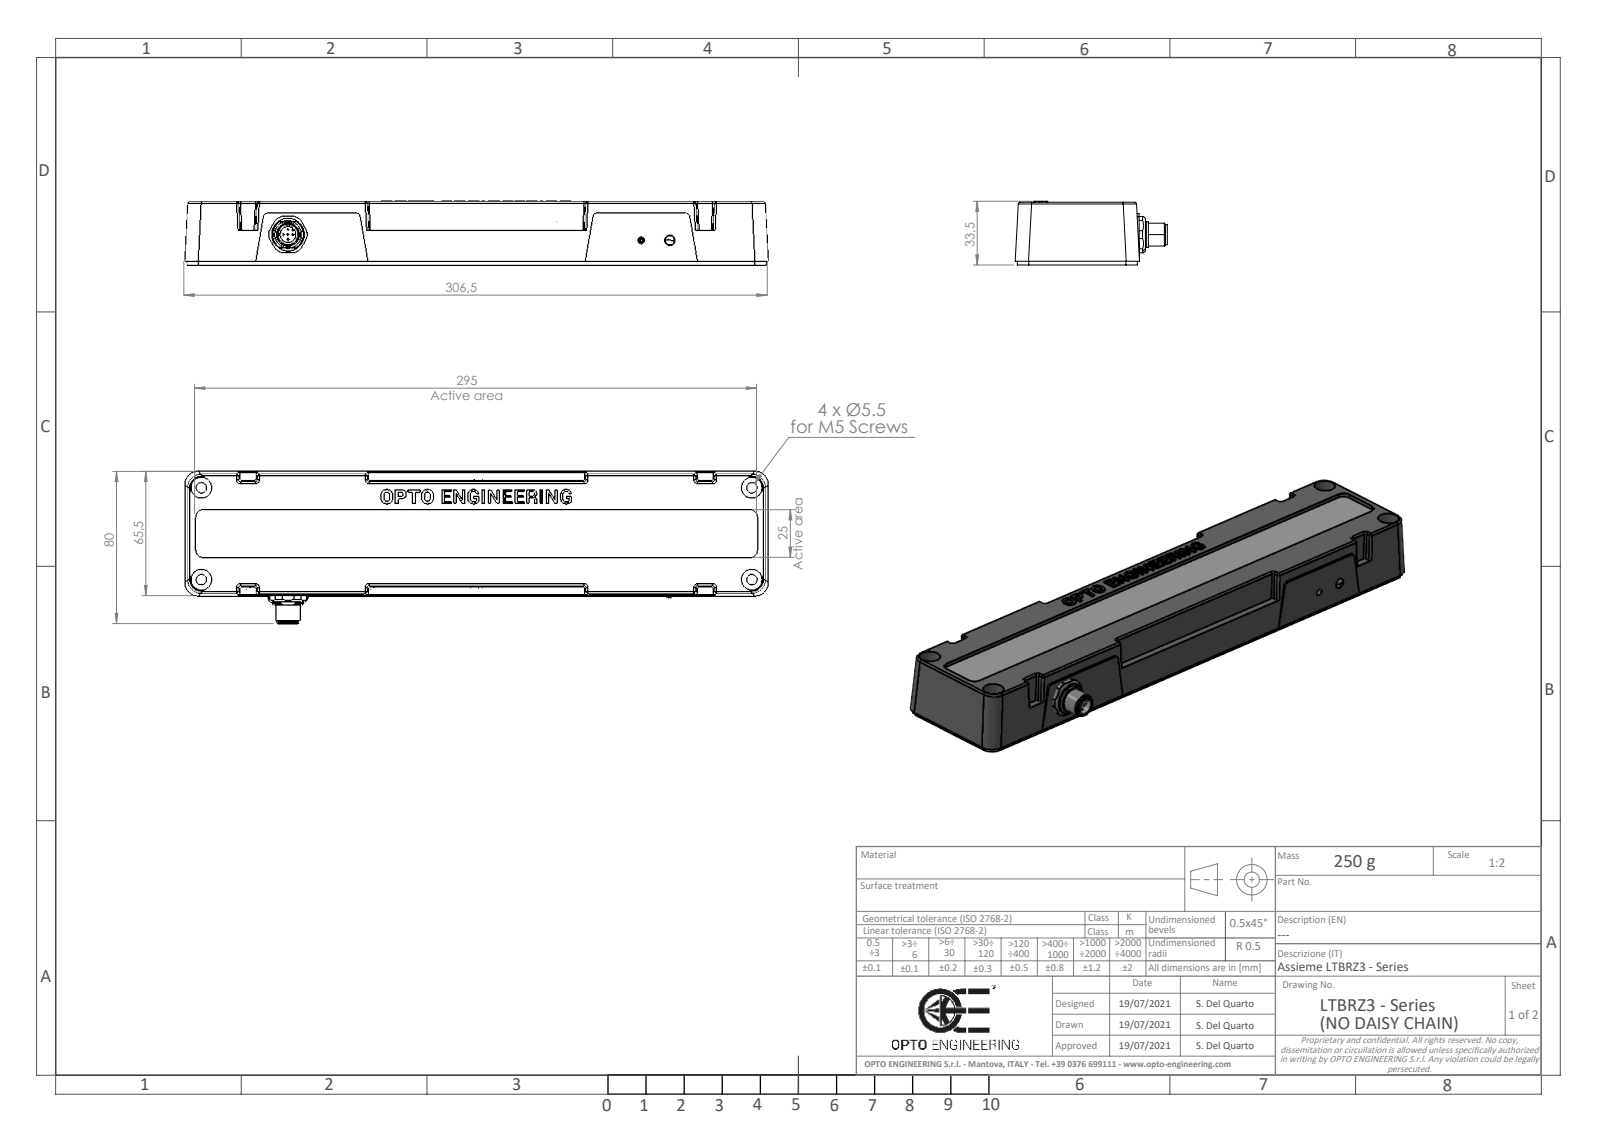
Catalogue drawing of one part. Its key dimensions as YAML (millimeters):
part_name: "OELTBRZ300_ASSY_NO_DAISY_CHAIN"
step_written_by: "SolidWorks 2020 (AUTOMOTIVE_DESIGN)"
units: millimeters
bodies: {solids: 0, faces: 570, planar: 225, cylindrical: 211, other: 134}
overall_size: [306.25, 79.88, 33.5]
round_holes:
  - {diameter: 5.5, count: 5}
  - {diameter: 3.5, count: 1}
  - {diameter: 8.3, count: 1}
round_bosses_or_shafts:
  - {diameter: 5.5, count: 10}
  - {diameter: 1, count: 5}
  - {diameter: 12, count: 1}
  - {diameter: 10.5, count: 1}
partial_cylinders:
  - {radius: 0.55, count: 60}
  - {radius: 0.25, count: 48}
  - {radius: 1, count: 36}
  - {radius: 2, count: 4}
  - {radius: 4, count: 4}
  - {radius: 6, count: 4}
  - {radius: 7, count: 4}
  - {radius: 0.5, count: 2}
face_to_face_distances: [31, 2, 33, 4, 3, 28, 30, 15, 19, 44]
hole_center_spacings: [48, 289, 292.96, 15]
